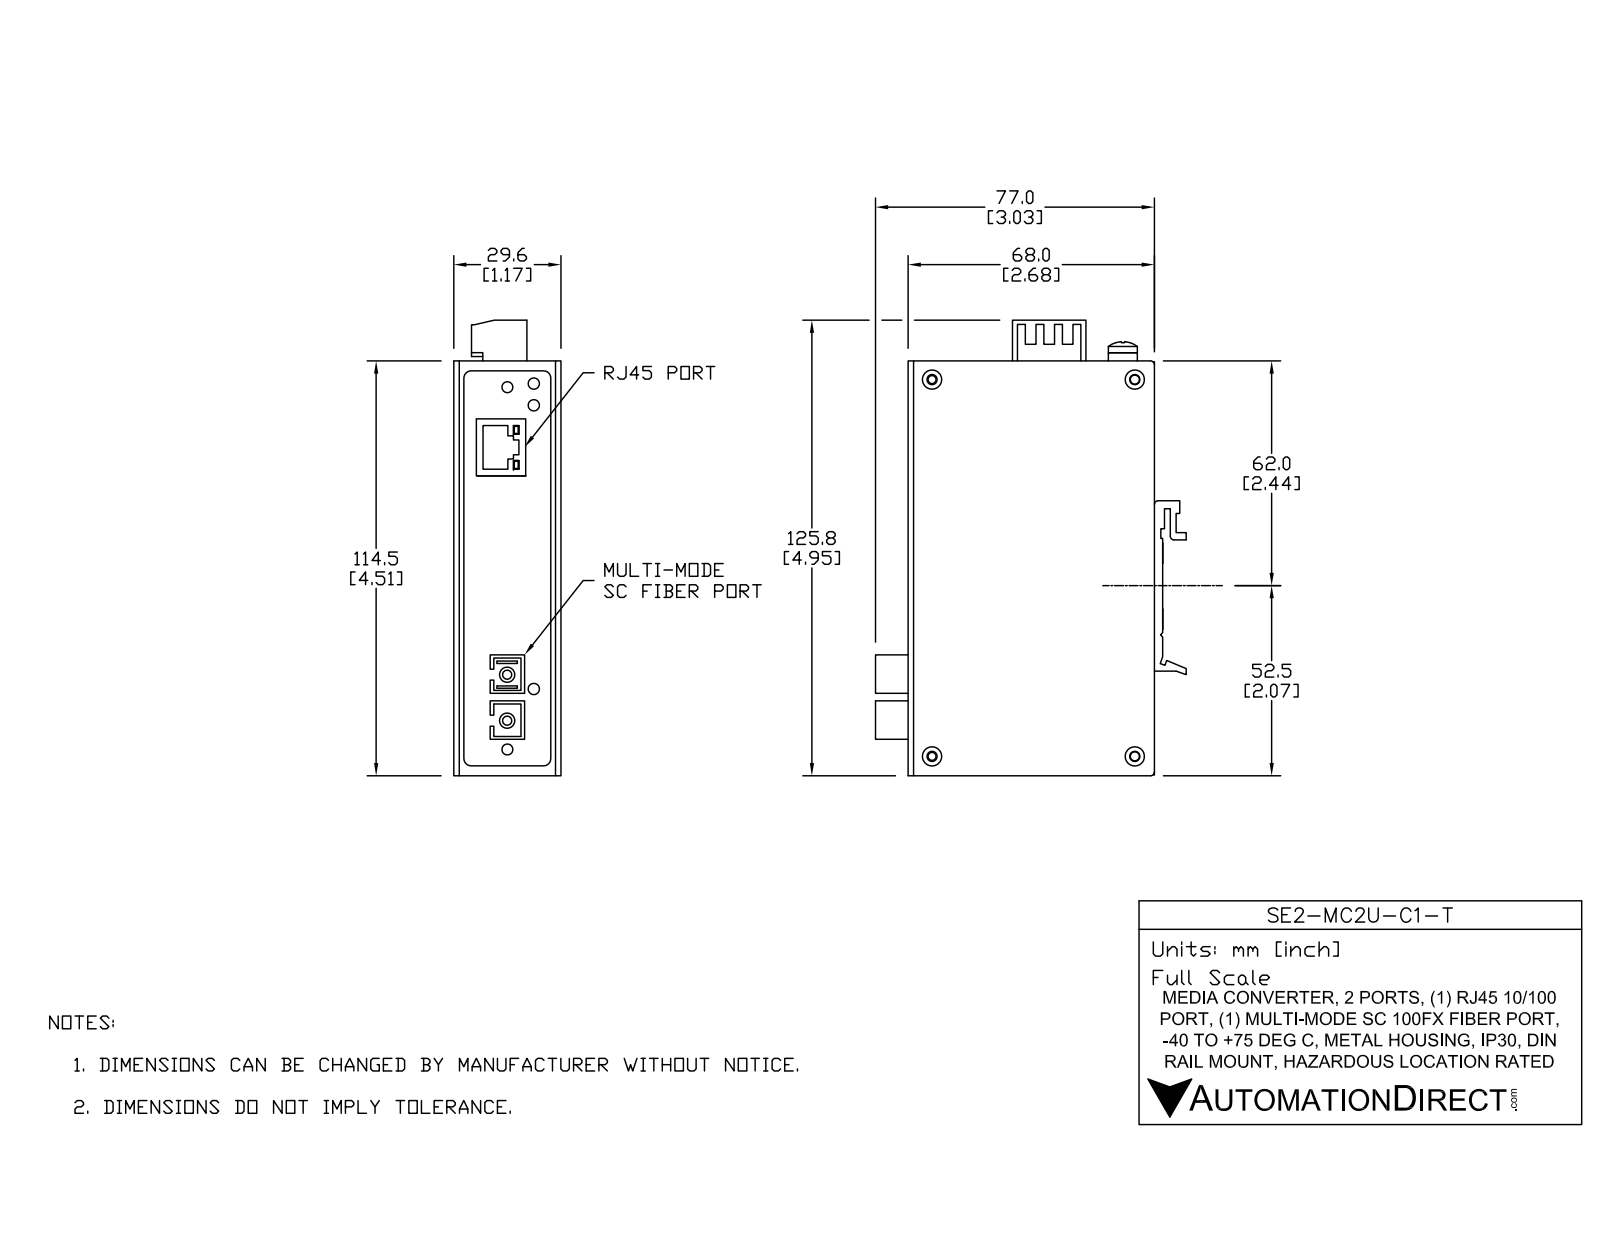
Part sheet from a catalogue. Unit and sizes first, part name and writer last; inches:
Units: inches
Overall size (bounding box): 4.951 × 3.379 × 1.165
Round holes (diameter × count): ⌀0.11 ×4, ⌀0.15 ×4, ⌀0.122 ×3, ⌀0.099 ×2, ⌀0.118 ×2, ⌀0.134 ×2, ⌀0.155 ×2
Round bosses / shafts (diameter × count): ⌀0.142 ×4, ⌀0.217 ×2, ⌀0.197 ×2, ⌀0.165 ×2, ⌀0.118 ×2, ⌀0.315 ×1, ⌀0.157 ×1
Partial cylindrical surfaces — rounded edges, fillets, slot ends (radius × count): R0.024 ×192, R0.026 ×32, R0.041 ×8, R0.079 ×8, R0.118 ×8, R0.008 ×6, R0.039 ×5, R0.012 ×4
Main face-to-face distances: 0.039, 0.02, 1.087, 1.126, 0.079, 1.047, 1.106, 1.067, 0.04, 0.059
Hole centre spacings: 0.203, 0.4, 2.205, 4.094, 4.65, 0.197, 0.236, 0.29
Volume: 3.605 in³ · Surface area: 175.2 in²
Bodies: 16 solids, 1091 faces (693 planar, 351 cylindrical, 47 other)
Part name (STEP PRODUCT): SE2-MC2U-C1-T
STEP written by: SolidWorks 2017 (AUTOMOTIVE_DESIGN)
